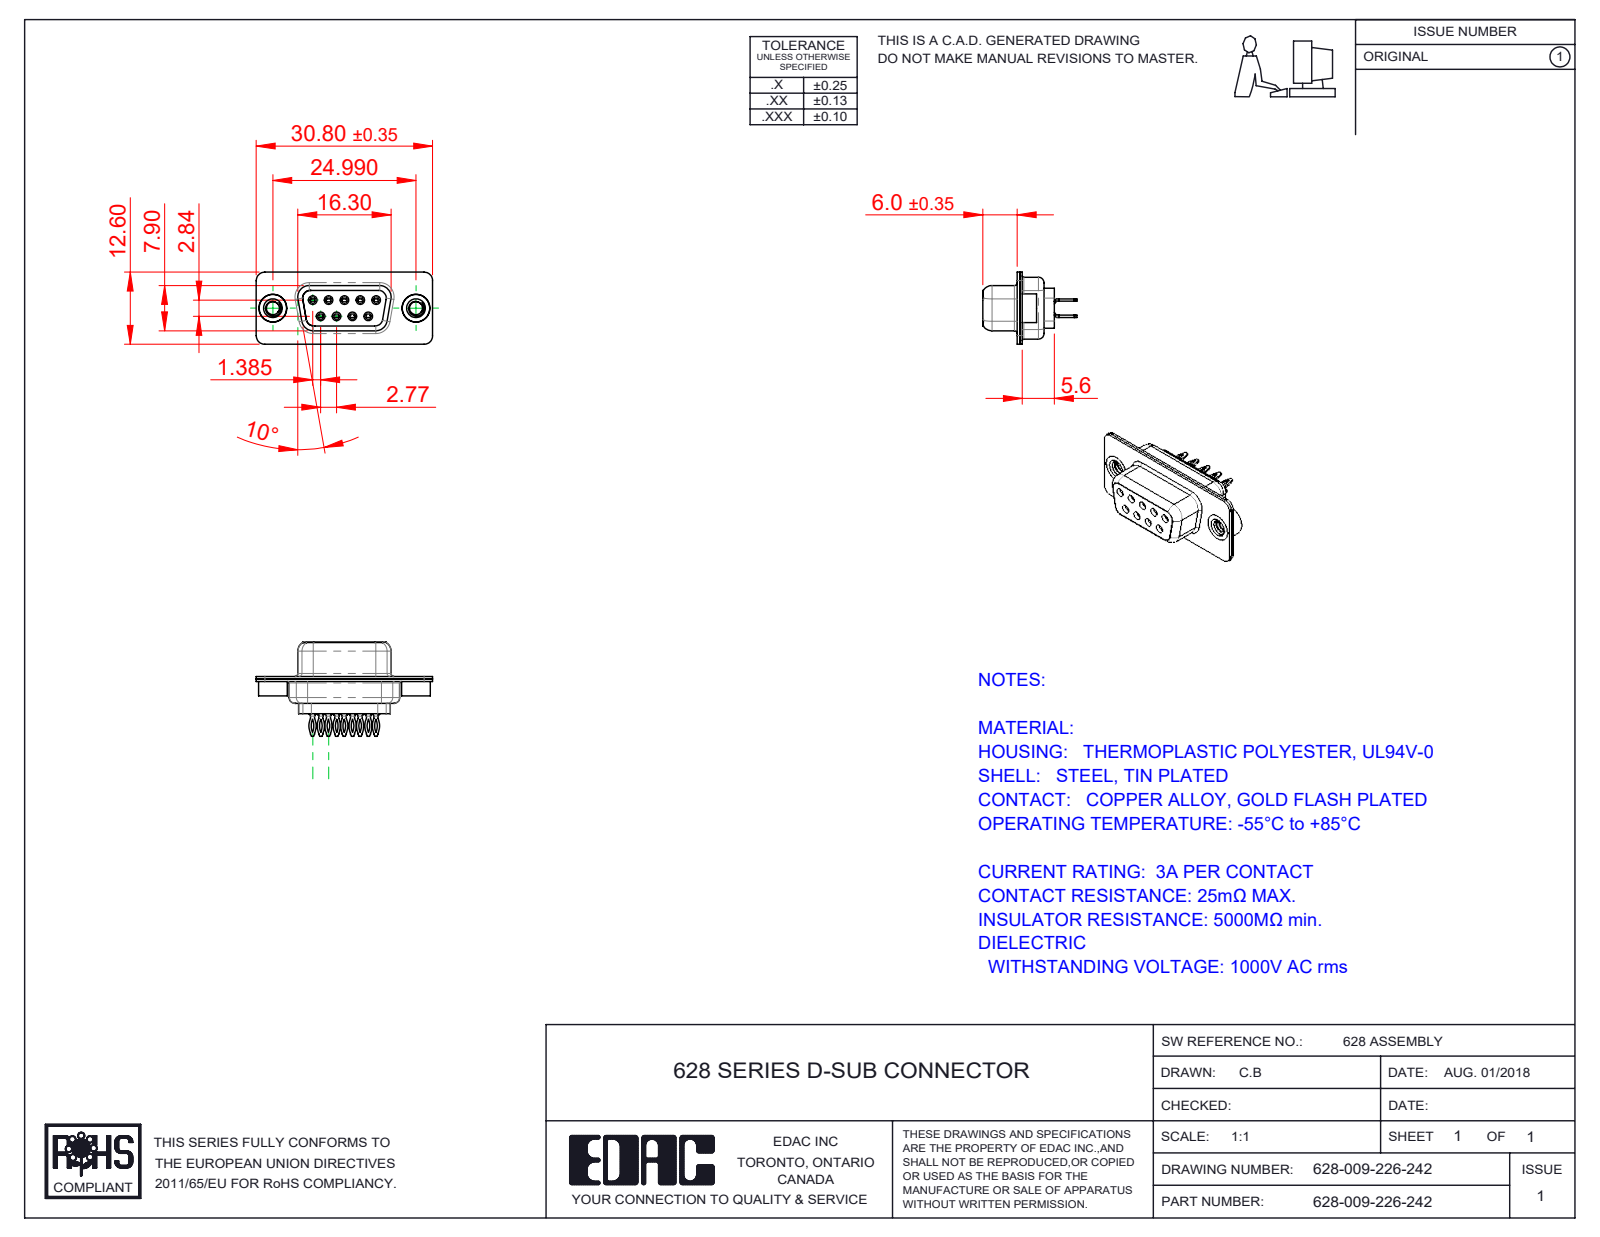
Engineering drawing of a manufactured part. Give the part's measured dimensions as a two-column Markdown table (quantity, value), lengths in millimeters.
| quantity | value |
| --- | --- |
| part name | 628 Contact Row 1_26L; 628 Contact Row 2_26L; 628 Shell Front_09 Contacts; 628-009-226-242 (+3 more) |
| STEP written by | SolidWorks 2020 (CONFIG_CONTROL_DESIGN) |
| units | millimeters |
| bodies | 14 solids, 1184 faces (310 planar, 378 cylindrical, 496 other) |
| overall size | 30.8 × 16.45 × 12.6 |
| volume | 1 753 mm³ |
| surface area | 4 467 mm² |
| round holes (diameter × count) | 0.8 × 9, 0.9 × 9, 1.1 × 9, 1.6 × 9, 1.7 × 5, 2.26 × 2, 4 × 2, 4.05 × 2, 4.85 × 2 |
| round bosses / shafts (diameter × count) | 2 × 9, 1.5 × 9, 1.2 × 9, 5 × 2, 4.95 × 2, 4.8 × 2 |
| partial cylindrical surfaces (radius × count) | 2.92 × 18, 3.33 × 18, 1.5 × 17, 2 × 12, 0.28 × 9, 1.35 × 6, 0.25 × 4, 0.5 × 4 |
| main face-to-face distances | 0.45, 0.4, 0.9, 1.9, 8.5, 6.6, 1.4, 0.5, 7.05, 0.85 |
| hole center spacings | 3.16, 2.77, 5.54, 5.03, 5.04, 8.31, 7.48, 7.49 |
